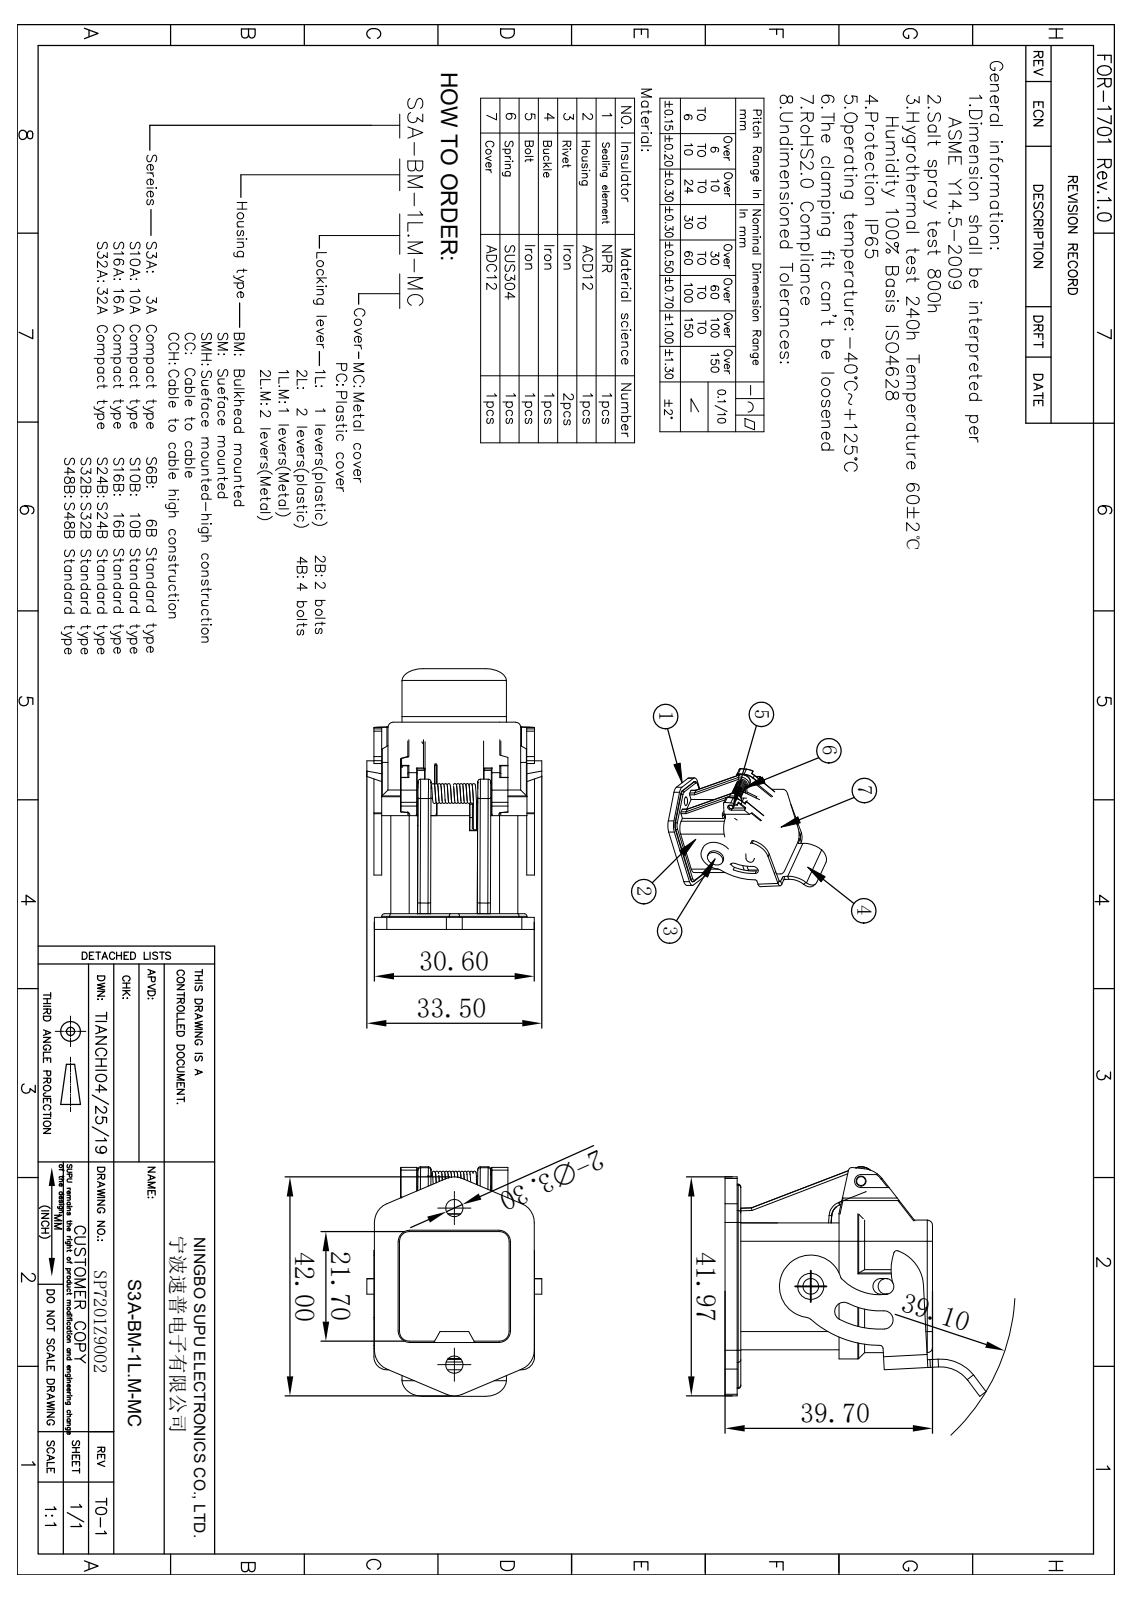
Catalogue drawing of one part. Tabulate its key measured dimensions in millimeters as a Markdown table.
| quantity | value |
| --- | --- |
| part name | SUPU3144BDEE1cej |
| STEP written by | SIEMENS PLM Software NX 10.0 (AUTOMOTIVE_DESIGN) |
| units | millimeters |
| bodies | 2 solids, 565 faces (164 planar, 218 cylindrical, 183 other) |
| overall size | 60.85 × 58.66 × 34.3 |
| volume | 10 582 mm³ |
| surface area | 14 195 mm² |
| round holes (diameter × count) | 3.4 × 3, 3.1 × 2, 2.05 × 1, 2.3 × 1, 6 × 1 |
| round bosses / shafts (diameter × count) | 7.2 × 1, 4.4 × 1, 3 × 1, 2.1 × 1 |
| partial cylindrical surfaces (radius × count) | 0.2 × 73, 0.3 × 13, 0.35 × 9, 2 × 8, 0.9 × 6, 1 × 6, 0.6 × 4, 2.1 × 4 |
| main face-to-face distances | 1.4, 1.5, 23.9, 2.55, 26.45, 4.05, 27.95, 30.5, 32, 20.5 |
| hole center spacings | 22.12, 29.9, 30 |
